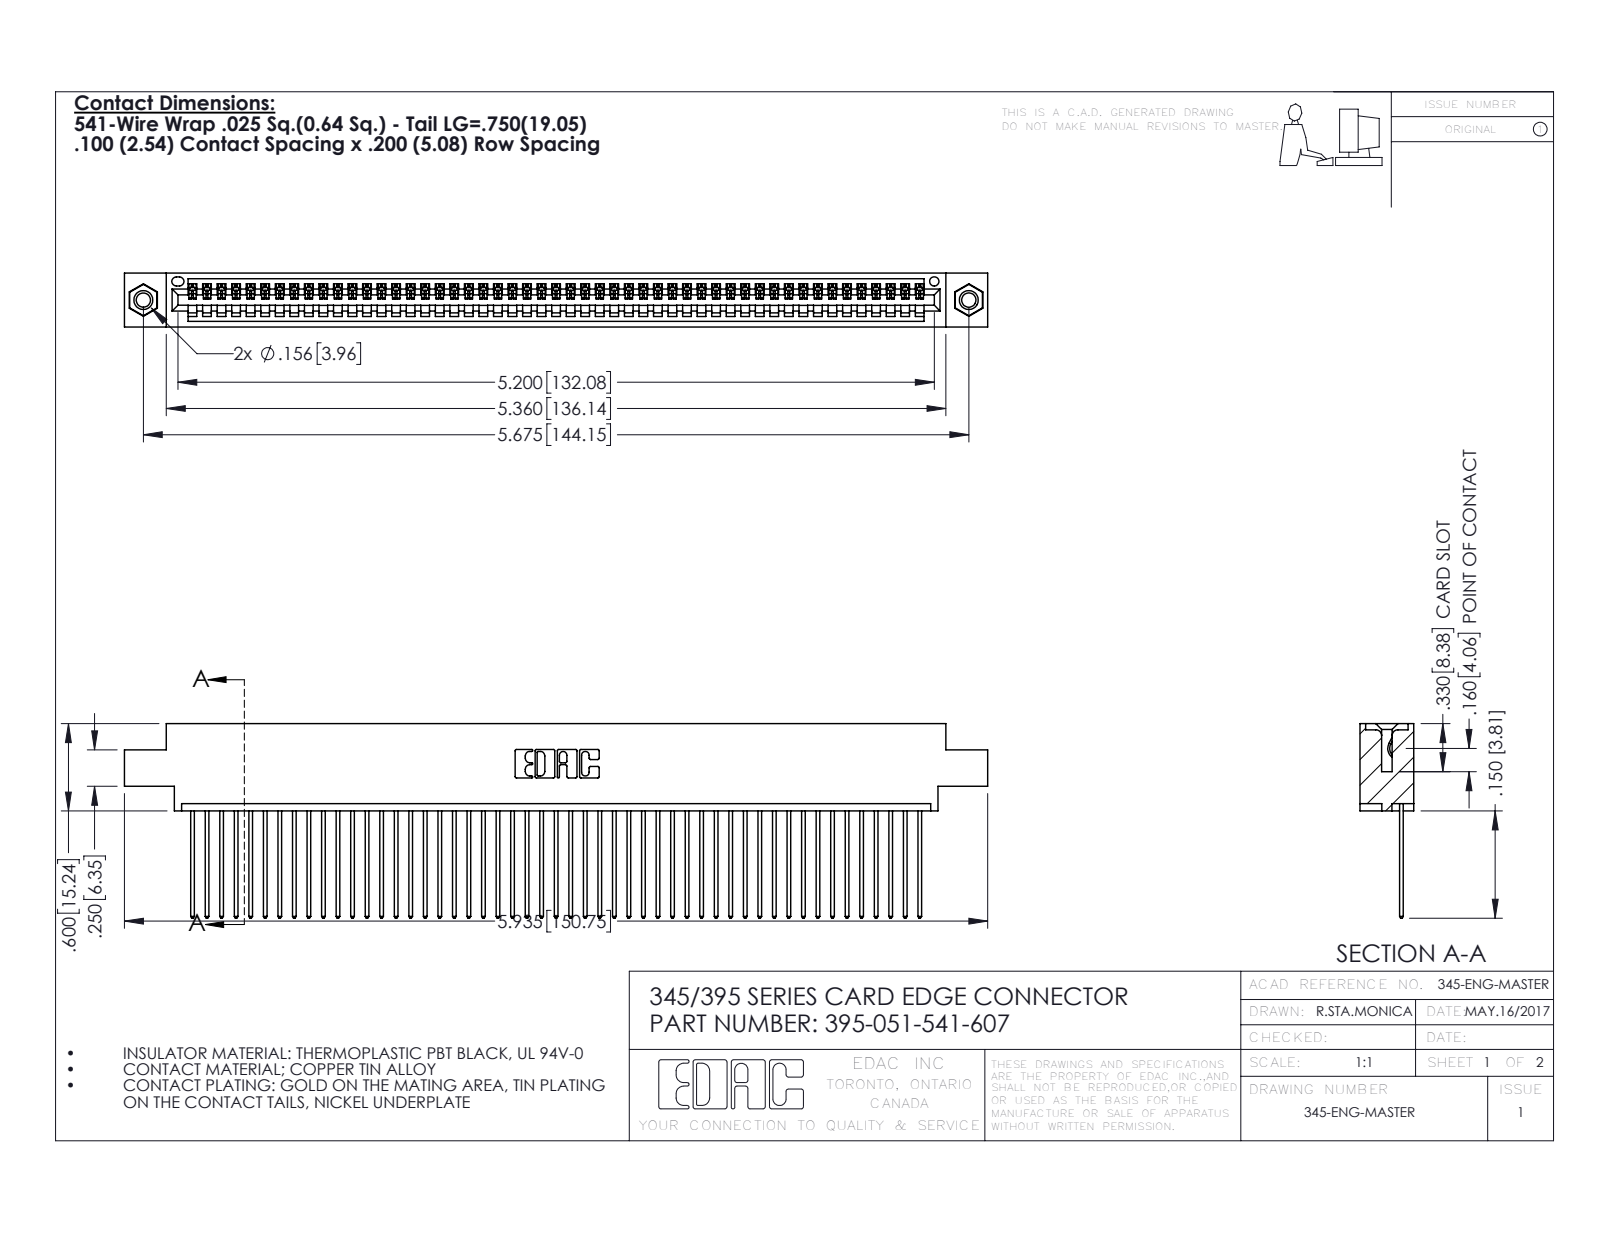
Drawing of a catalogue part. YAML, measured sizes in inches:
part_name: "345 Part_0.170 Offset - 0.156 Dia-TI; 345-292-001_345-293-141; 345-250-001_345-250-005-103; 395-051-541-607"
step_written_by: "SolidWorks 2016 (CONFIG_CONTROL_DESIGN)"
units: inches
bodies: {solids: 54, faces: 3148, planar: 2156, cylindrical: 976, other: 16}
overall_size: [5.935, 1.337, 0.37]
volume: 0.881
surface_area: 31.7
round_holes:
  - {diameter: 0.098, count: 2}
  - {diameter: 0.125, count: 2}
  - {diameter: 0.156, count: 2}
  - {diameter: 0.064, count: 1}
round_bosses_or_shafts:
  - {diameter: 0.155, count: 2}
partial_cylinders:
  - {radius: 0.006, count: 102}
  - {radius: 0.01, count: 102}
  - {radius: 0.01, count: 22}
  - {radius: 0.007, count: 6}
  - {radius: 0.031, count: 6}
  - {radius: 0.026, count: 3}
  - {radius: 0.031, count: 2}
  - {radius: 0.04, count: 2}
face_to_face_distances: [0.072, 0.298, 0.098, 0.272, 0.025, 0.37, 0.2, 0.225, 0.175, 0.149]
hole_center_spacings: [0.27, 5.439, 5.675]
